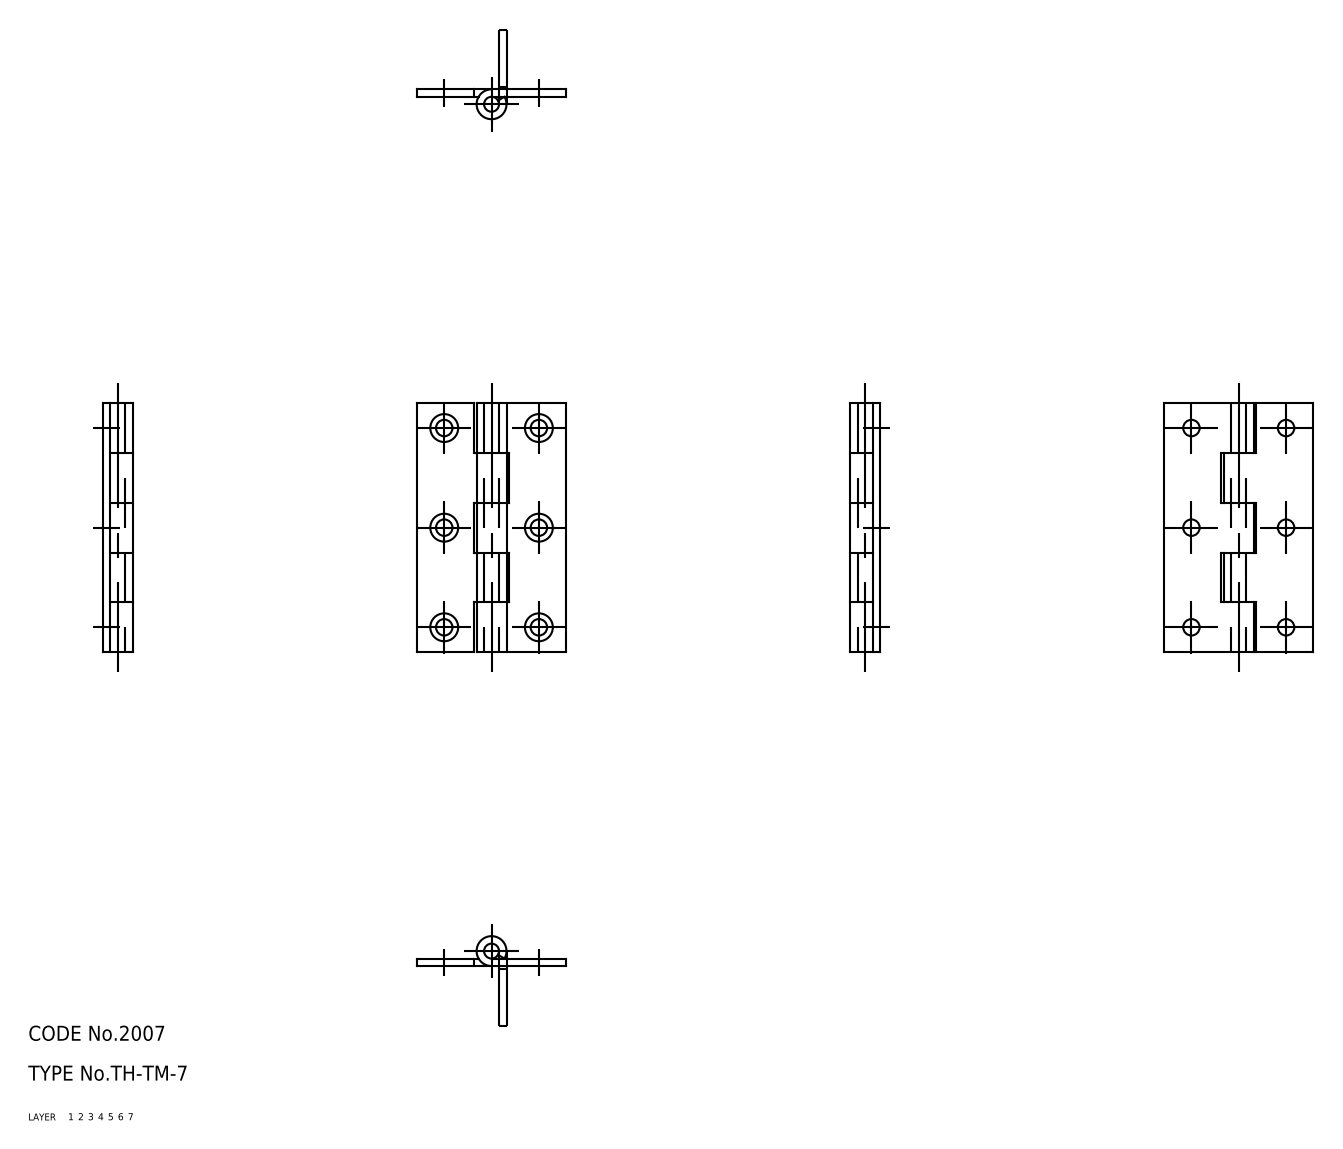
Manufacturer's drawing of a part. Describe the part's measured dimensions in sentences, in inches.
The part is named "shaft; hinge piece_B; hinge piece_A; TH_TM_7_25044_36". Its 3-D file was written by "CADfix (AUTOMOTIVE_DESIGN)". It is 3 solids with 66 faces: 0 planar, 0 cylindrical and 66 other. Overall it measures 1.969 by 1.181 by 0.236 inches. Its volume is 0.189 cubic inches and its surface area 7.544 square inches.
